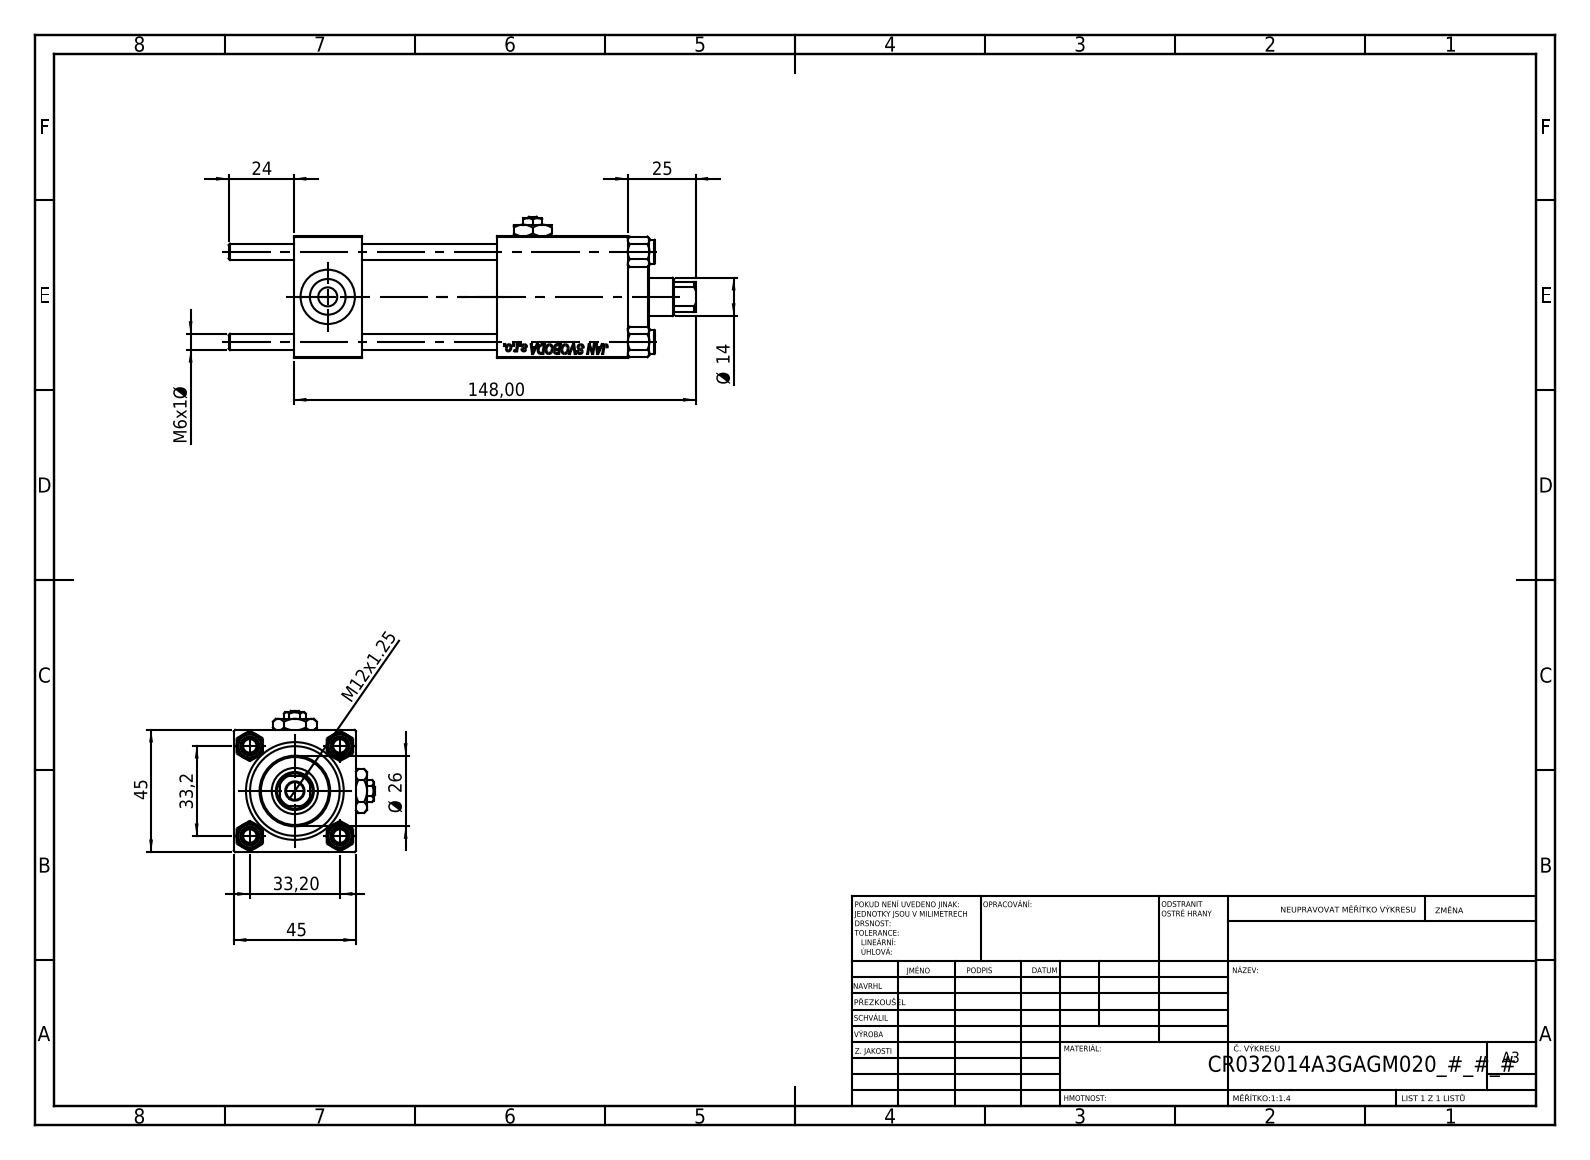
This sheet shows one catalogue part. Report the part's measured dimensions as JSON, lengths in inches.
{"part_name": "V215_VC_A; CR025_012_A_0_G_A_G_M_020_+#_##_TYCINKA; V215CR_BODY_A; NUT_M5 (+2 more)", "step_written_by": "SolidWorks 2019 (CONFIG_CONTROL_DESIGN)", "units": "inches", "bodies": {"solids": 13, "faces": 1232, "planar": 564, "cylindrical": 90, "other": 578}, "overall_size": [6.772, 2.047, 2.047], "volume_in3": 11.98, "surface_area_in2": 115.8, "round_holes": [[0.236, 4], [0.276, 2], [0.518, 2], [0.787, 2], [0.256, 1], [0.512, 1], [0.551, 1], [0.669, 1], [0.945, 1], [1.26, 1], [1.299, 1]], "round_bosses_or_shafts": [[0.354, 4], [1.496, 1], [1.024, 1]], "partial_cylinders_radius": [[0.256, 1]], "face_to_face_distances": [1.772, 0.984, 4.843, 3.858, 1.969, 2.953, 1.89, 3.713, 2.728, 0.76], "hole_center_spacings": [0.924, 1.307, 1.848]}
